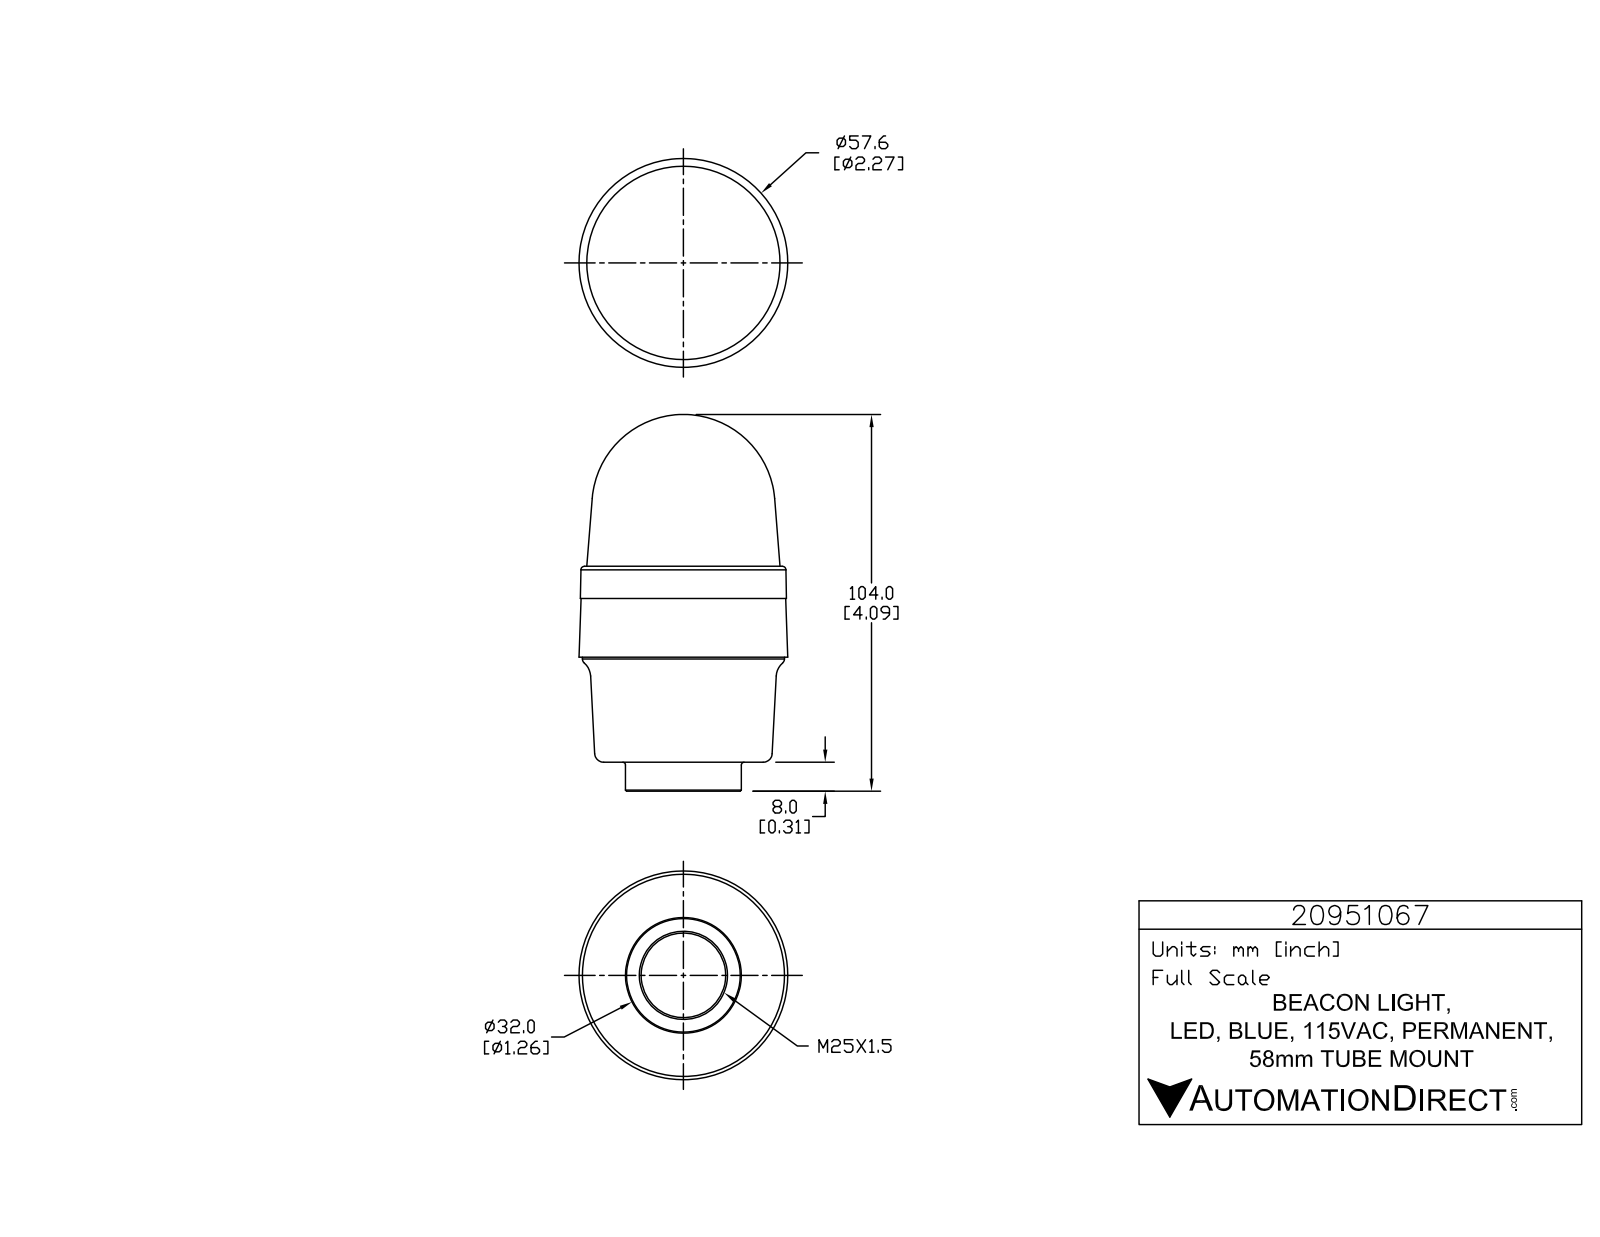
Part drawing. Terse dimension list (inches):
name: 20951067
written by: SolidWorks 2015 (AUTOMOTIVE_DESIGN)
unit: in
bodies: 1 solid, 791 faces (525 planar, 168 cylindrical, 98 other)
size: 4.051 × 2.269 × 2.269
volume: 11.72 in³; area: 29.93 in²
holes: 3× ⌀0.039, 1× ⌀0.92
bosses: 3× ⌀0.226, 3× ⌀0.056, 1× ⌀2.197, 1× ⌀1.26
rounds: 6× R0.008, 6× R0.008, 6× R0.008, 6× R0.131, 3× R0.004, 3× R0.005, 3× R0.008, 3× R0.008
face distances: 0.315, 1.142, 1.457, 0.988, 2.13, 2.445, 0.35, 0.638, 1.78, 2.094
